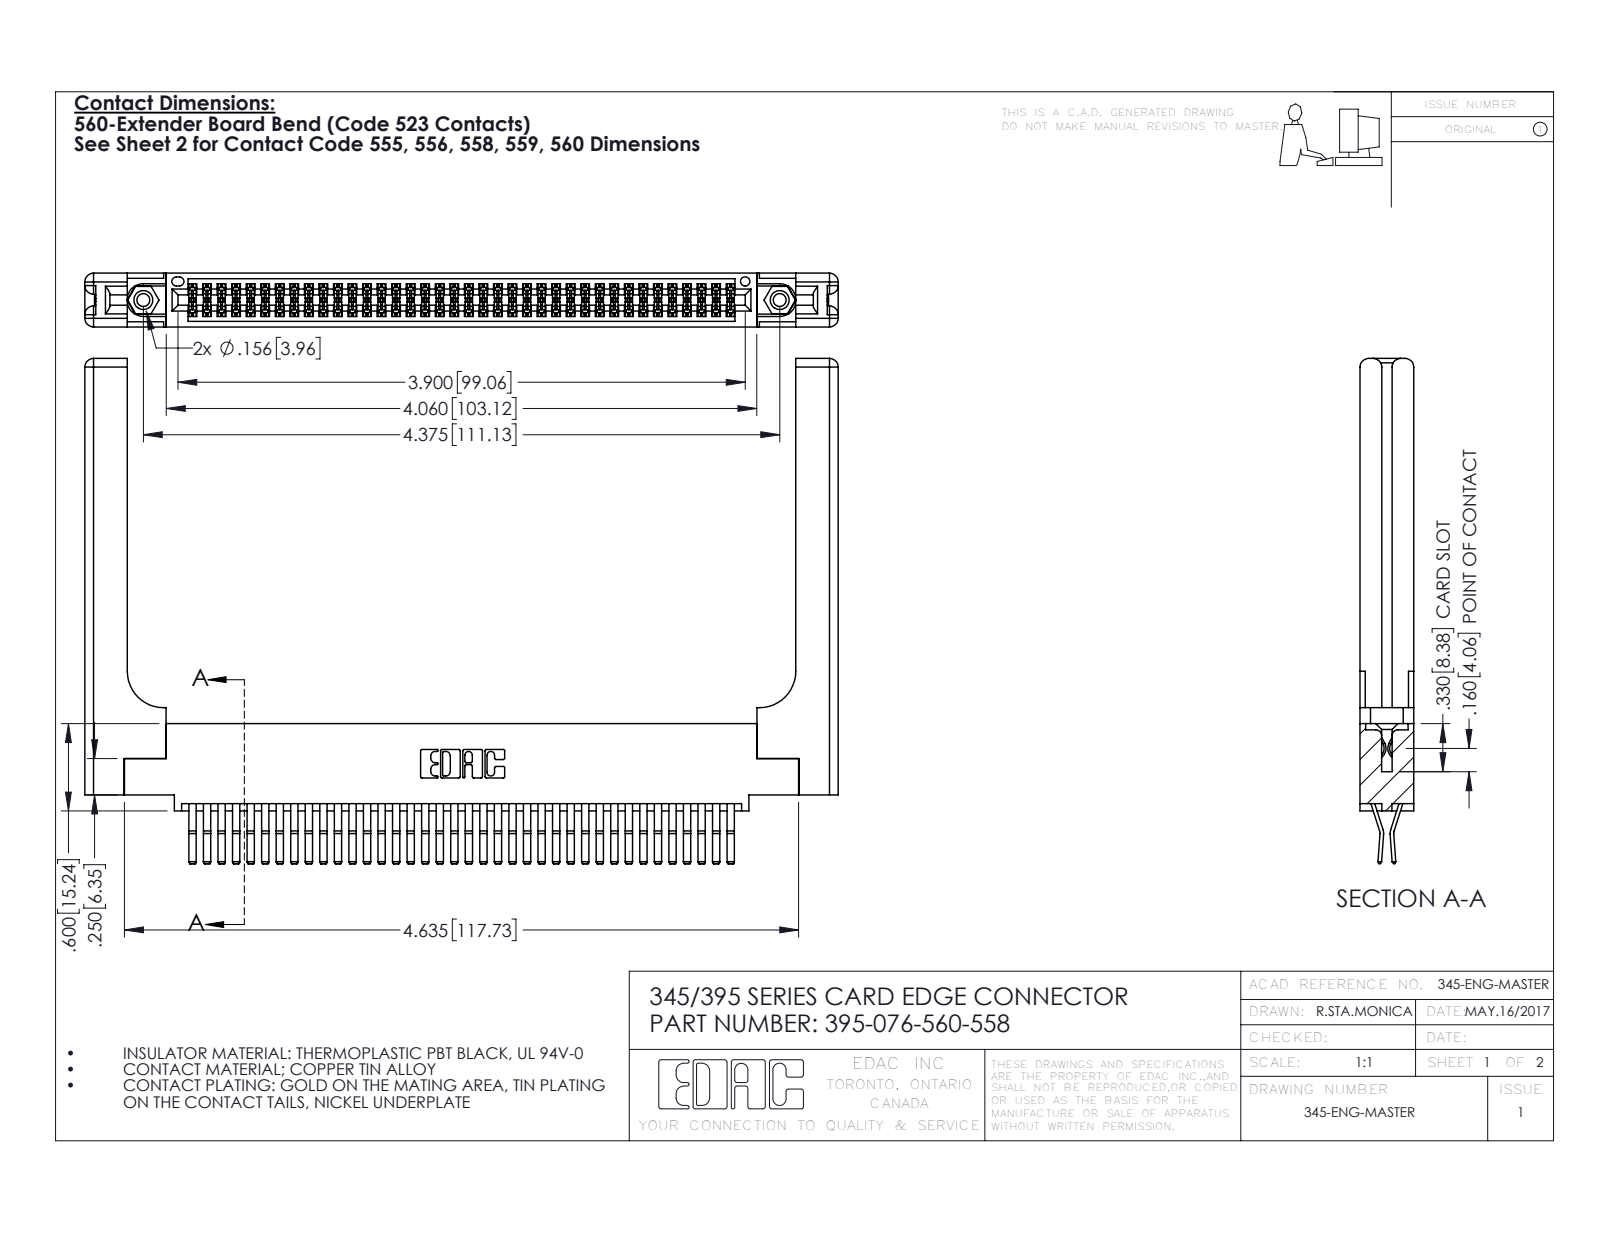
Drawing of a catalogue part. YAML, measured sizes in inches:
part_name: "395-076-560-558; 345-292-001_560 Tail; 345 Part_0.110 Offset - 0.156 Dia-TH; 345-220-058_345-220-058 (+1 more)"
step_written_by: "SolidWorks 2016 (CONFIG_CONTROL_DESIGN)"
units: inches
bodies: {solids: 81, faces: 4338, planar: 2740, cylindrical: 1538, other: 60}
overall_size: [5.179, 3.472, 0.37]
volume: 1.321
surface_area: 40.02
round_holes:
  - {diameter: 0.089, count: 2}
  - {diameter: 0.125, count: 2}
  - {diameter: 0.156, count: 2}
  - {diameter: 0.064, count: 1}
round_bosses_or_shafts:
  - {diameter: 0.155, count: 2}
partial_cylinders:
  - {radius: 0.006, count: 114}
  - {radius: 0.01, count: 22}
  - {radius: 0.06, count: 16}
  - {radius: 0.007, count: 6}
  - {radius: 0.031, count: 6}
  - {radius: 0.026, count: 3}
  - {radius: 0.01, count: 2}
  - {radius: 0.014, count: 2}
face_to_face_distances: [0.072, 0.37, 0.298, 0.025, 0.098, 0.272, 0.2, 0.225, 0.148, 0.15]
hole_center_spacings: [0.27, 4.139, 4.375]
